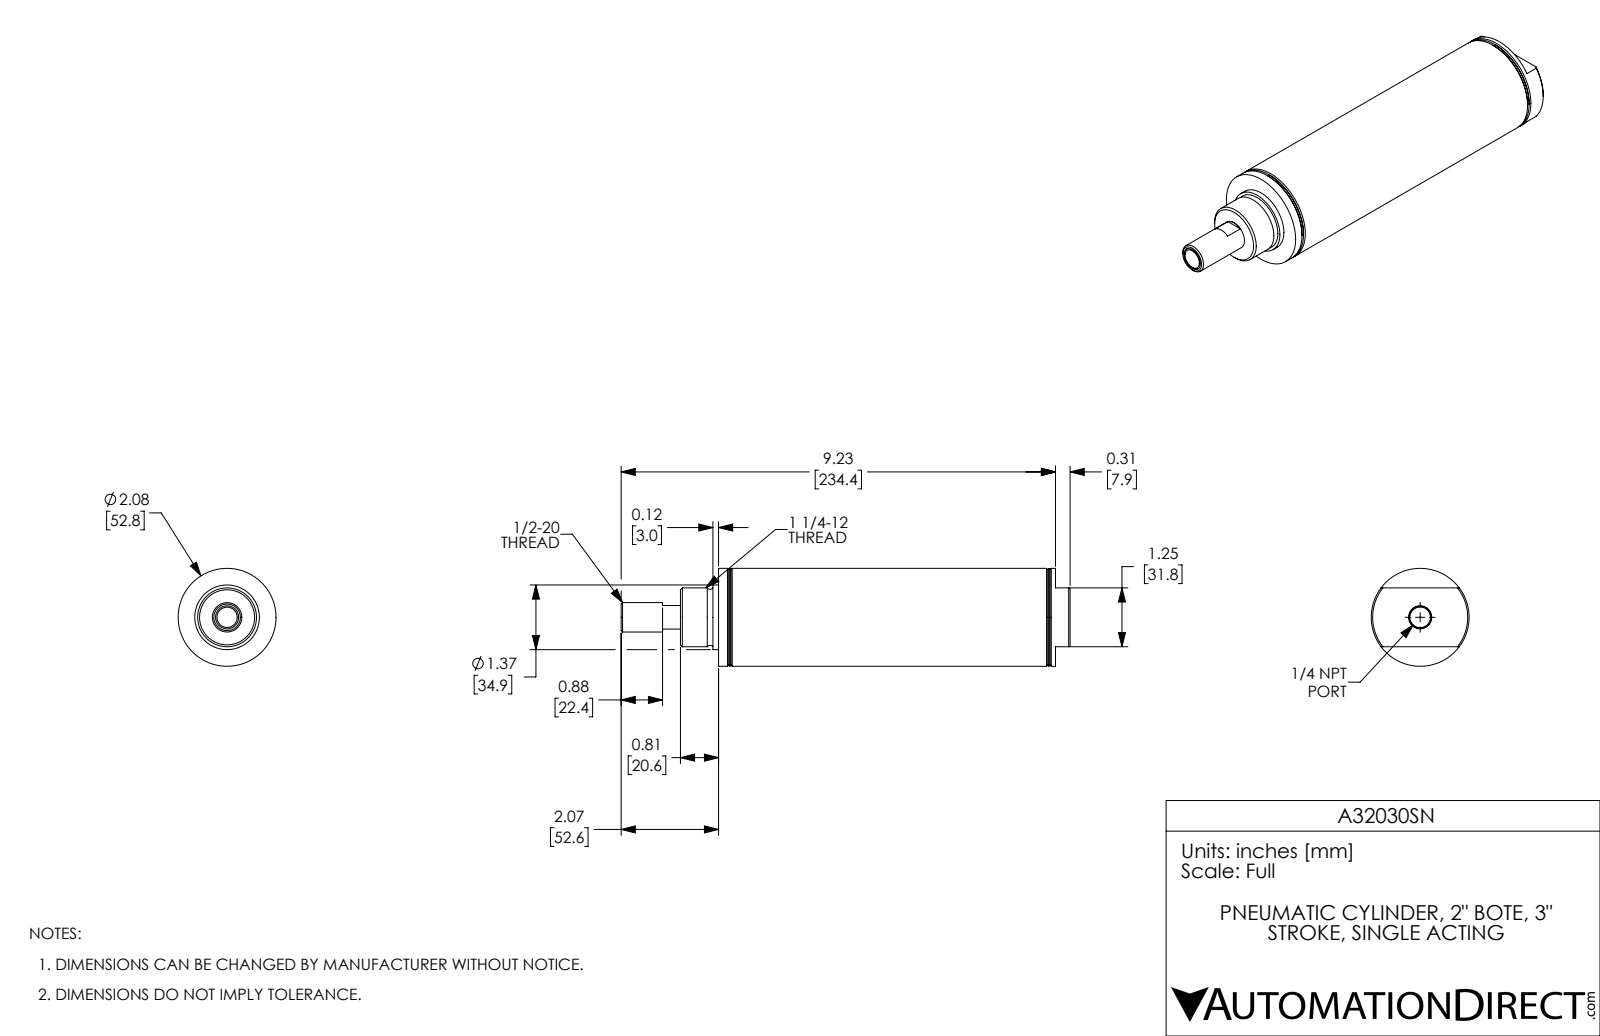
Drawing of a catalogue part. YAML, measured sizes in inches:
part_name: "A32030SN-Rod; A32030SN; A32030SN-MainBody"
step_written_by: "SolidWorks 2017 (AUTOMOTIVE_DESIGN)"
units: inches
bodies: {solids: 2, faces: 76, planar: 21, cylindrical: 22, other: 33}
overall_size: [9.54, 2.08, 2.08]
volume: 17.82
surface_area: 116.6
round_holes:
  - {diameter: 0.438, count: 1}
  - {diameter: 0.491, count: 1}
  - {diameter: 0.625, count: 1}
  - {diameter: 2, count: 1}
round_bosses_or_shafts:
  - {diameter: 2.08, count: 1}
  - {diameter: 1.373, count: 1}
  - {diameter: 1.25, count: 1}
face_to_face_distances: [0.5, 3.5, 3, 1.985, 2.485, 5.485, 7.47, 5.485, 4.985, 1.985]
